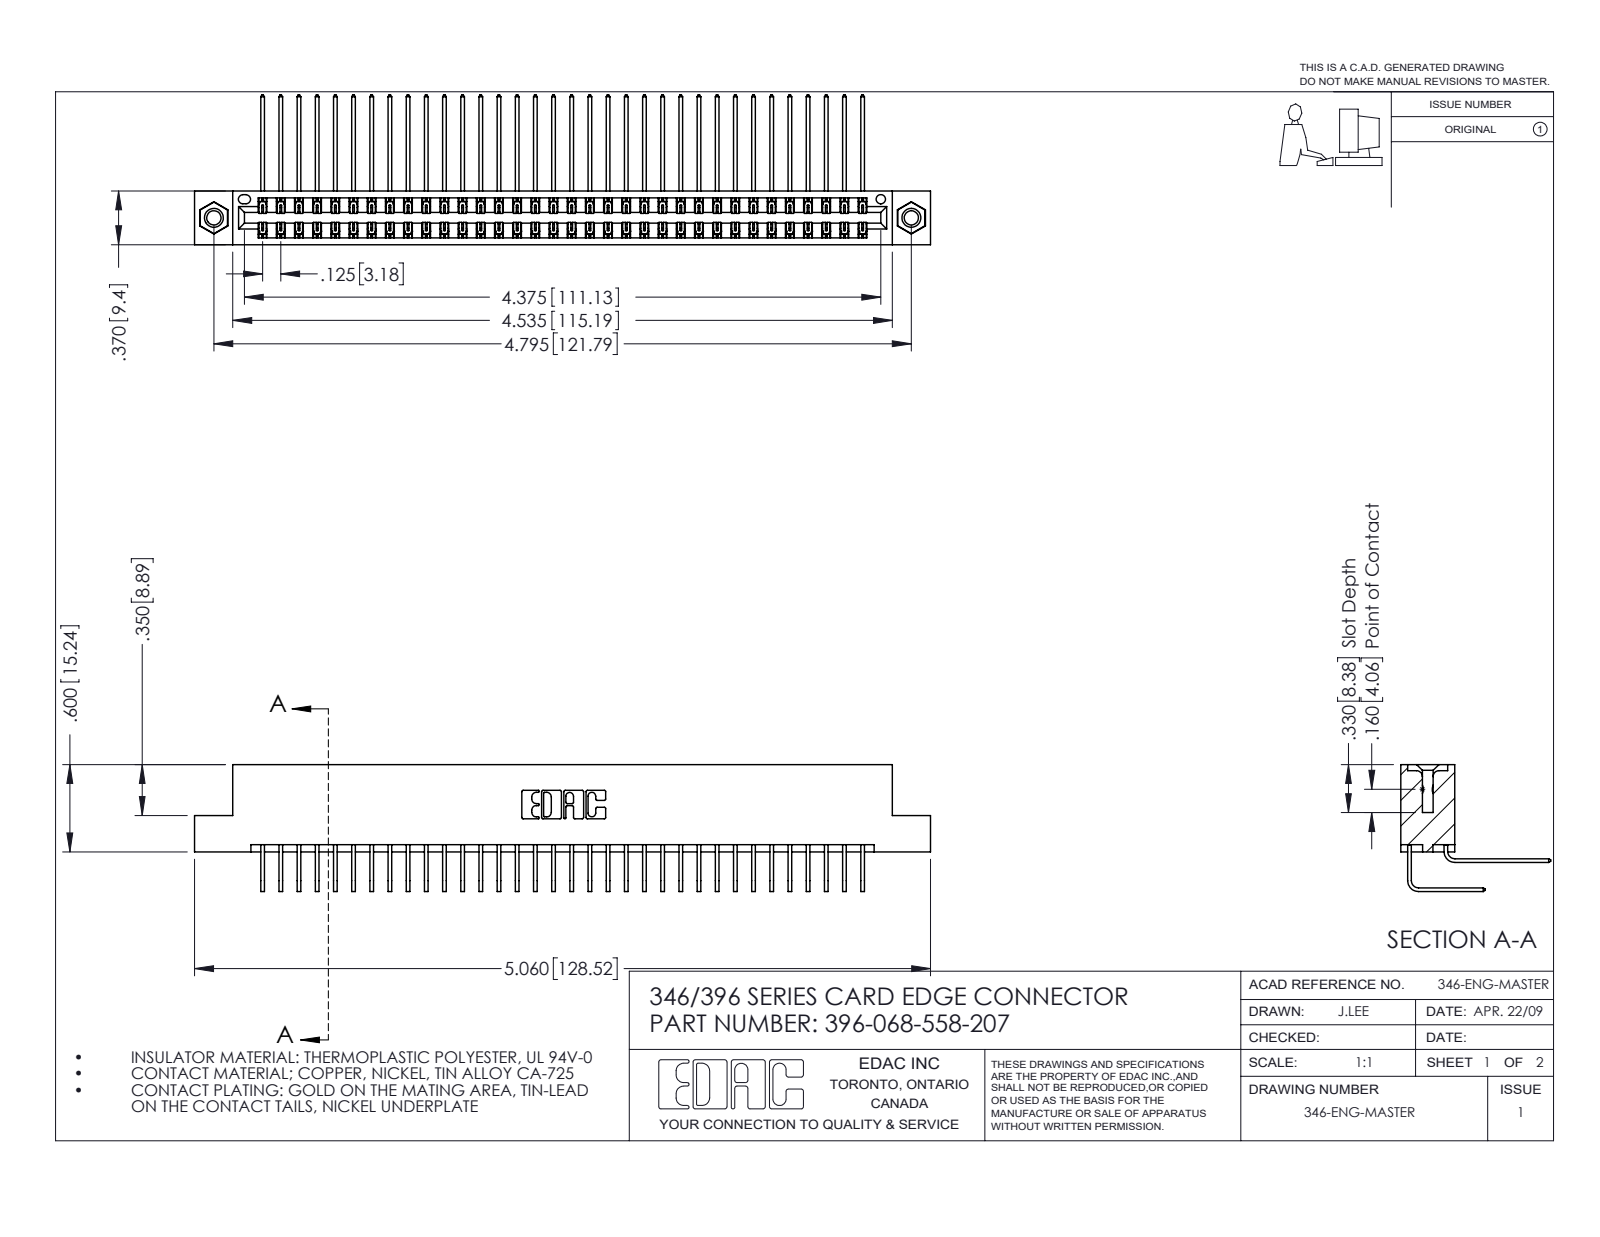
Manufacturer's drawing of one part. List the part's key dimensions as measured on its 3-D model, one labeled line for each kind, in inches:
Part name (STEP PRODUCT): 345-292-001_558 Tail - 2; 345-292-001_558 559 Tail - 1; 345-250-001_345-250-005-103; 396-068-558-207 (+1 more)
STEP written by: SolidWorks 2016 (CONFIG_CONTROL_DESIGN)
Units: inches
Bodies: 71 solids, 3854 faces (2624 planar, 1214 cylindrical, 16 other)
Overall size (bounding box): 5.06 × 1.03 × 0.873
Volume: 0.784 in³ · Surface area: 30.15 in²
Round holes (diameter × count): ⌀0.098 ×2, ⌀0.125 ×2, ⌀0.156 ×2, ⌀0.064 ×1
Round bosses / shafts (diameter × count): ⌀0.155 ×2
Partial cylindrical surfaces — rounded edges, fillets, slot ends (radius × count): R0.006 ×102, R0.01 ×22, R0.007 ×6, R0.031 ×6, R0.026 ×3, R0.014 ×2, R0.022 ×2, R0.024 ×2
Main face-to-face distances: 0.048, 0.322, 0.025, 0.25, 0.37, 0.072, 0.298, 0.275, 0.148, 0.222
Hole centre spacings: 0.246, 4.587, 4.795
